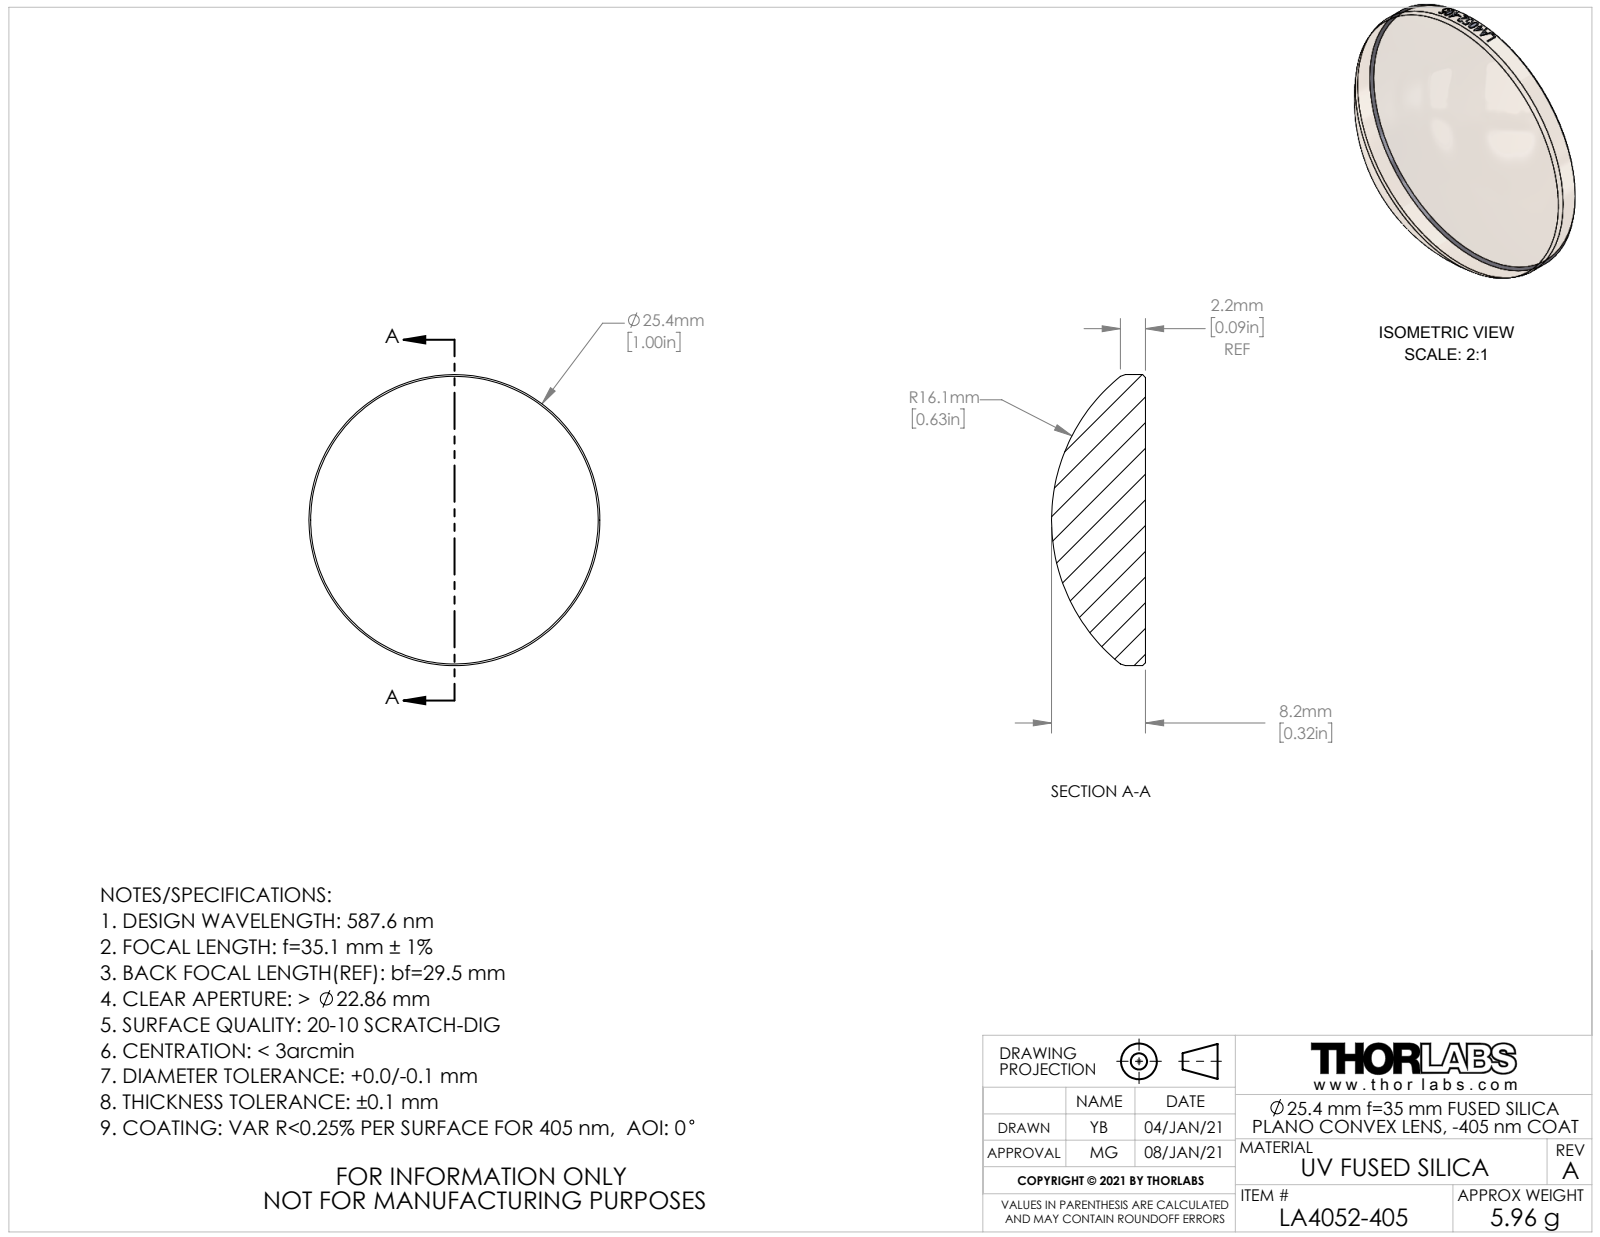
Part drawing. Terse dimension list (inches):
name: CTN016828-E0W; CTN016848
written by: SolidWorks 2018 (AUTOMOTIVE_DESIGN)
unit: in
bodies: 1 solid, 24 faces (1 planar, 17 cylindrical, 6 other)
size: 1 × 1 × 0.323
volume: 0.165 in³; area: 1.983 in²
bosses: 1× ⌀1
